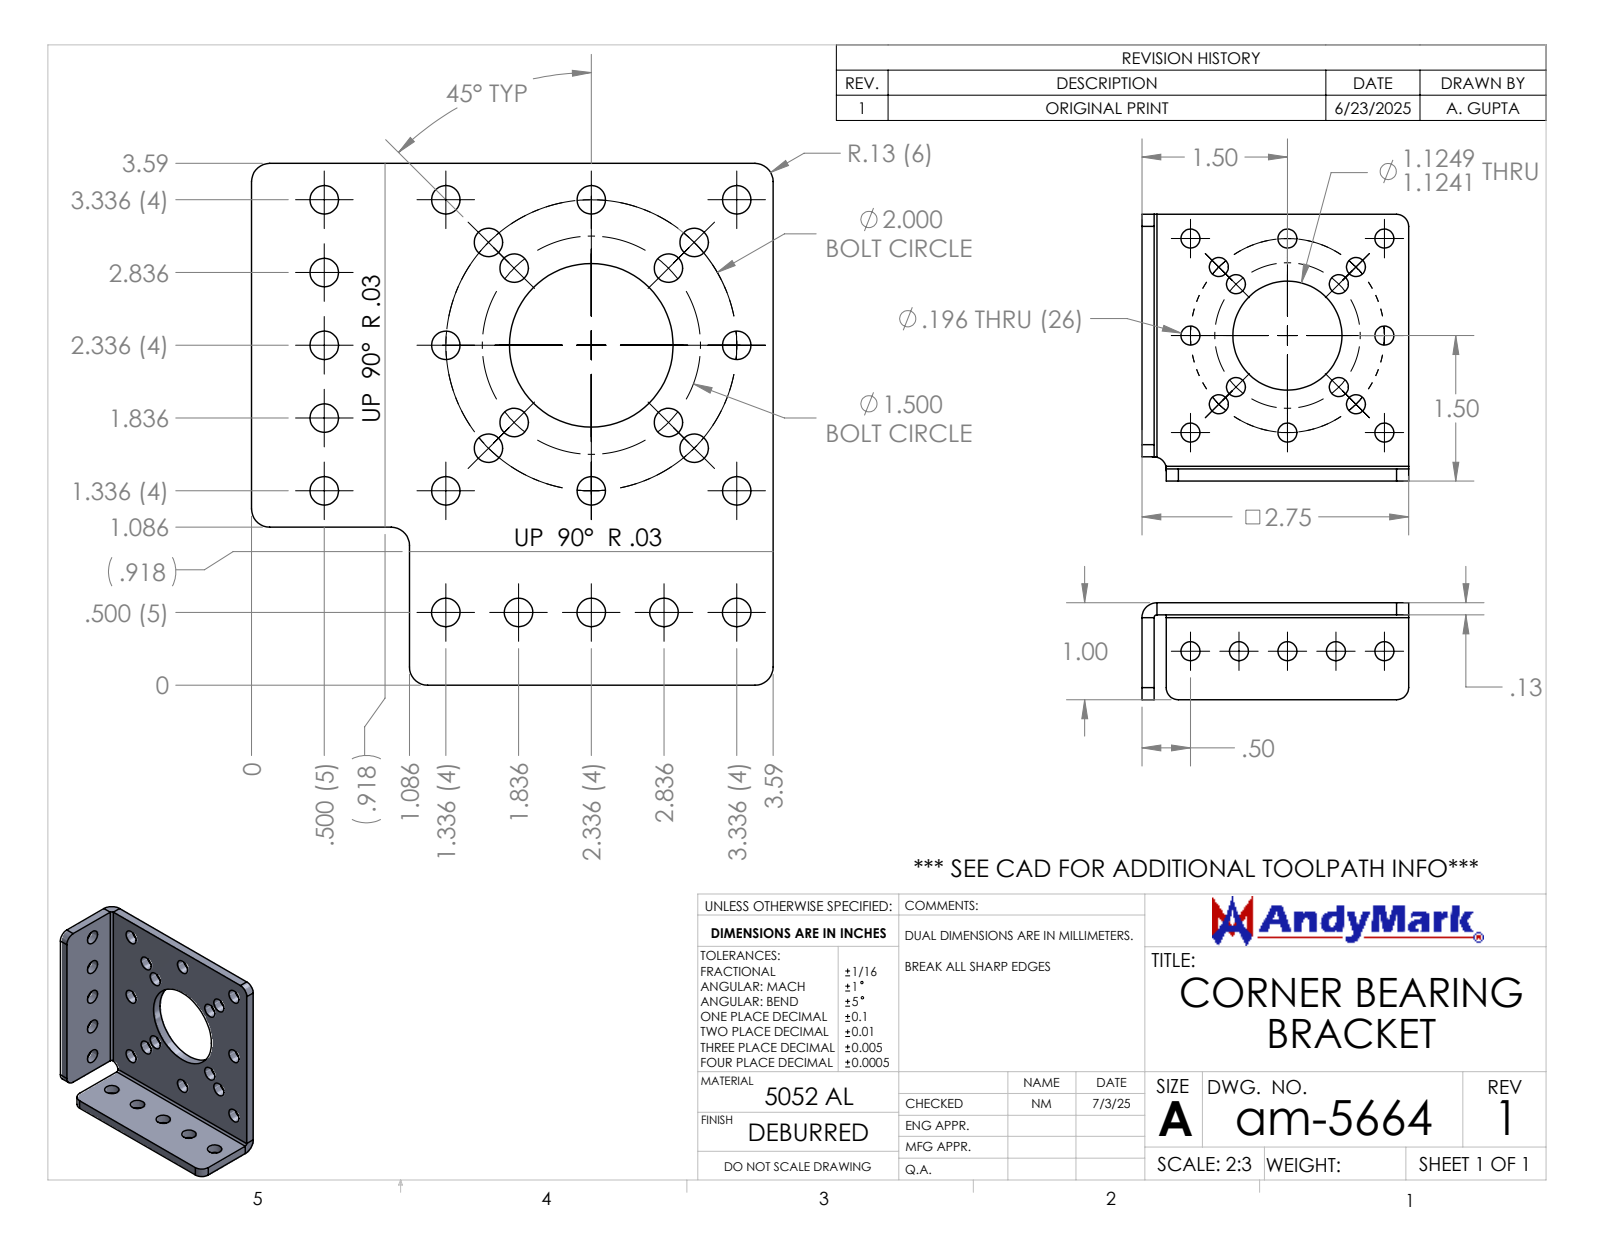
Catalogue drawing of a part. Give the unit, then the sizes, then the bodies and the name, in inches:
Units: inches
Overall size (bounding box): 2.75 × 2.75 × 1
Round holes (diameter × count): ⌀0.196 ×26, ⌀1.124 ×1
Partial cylindrical surfaces — rounded edges, fillets, slot ends (radius × count): R0.125 ×6, R0.029 ×2, R0.154 ×2
Main face-to-face distances: 0.125, 0.125, 2.75, 1, 0.875, 2.625, 2.625, 0.25, 2.5
Hole centre spacings: 1, 1.414, 2, 0.5, 0.708, 0.765, 1.25, 1.601
Volume: 1.236 in³ · Surface area: 23.97 in²
Bodies: 1 solid, 84 faces (18 planar, 64 cylindrical, 2 other)
Part name (STEP PRODUCT): am-5664 Corner Bearing Bracket
STEP written by: SolidWorks 2024 (AUTOMOTIVE_DESIGN)
